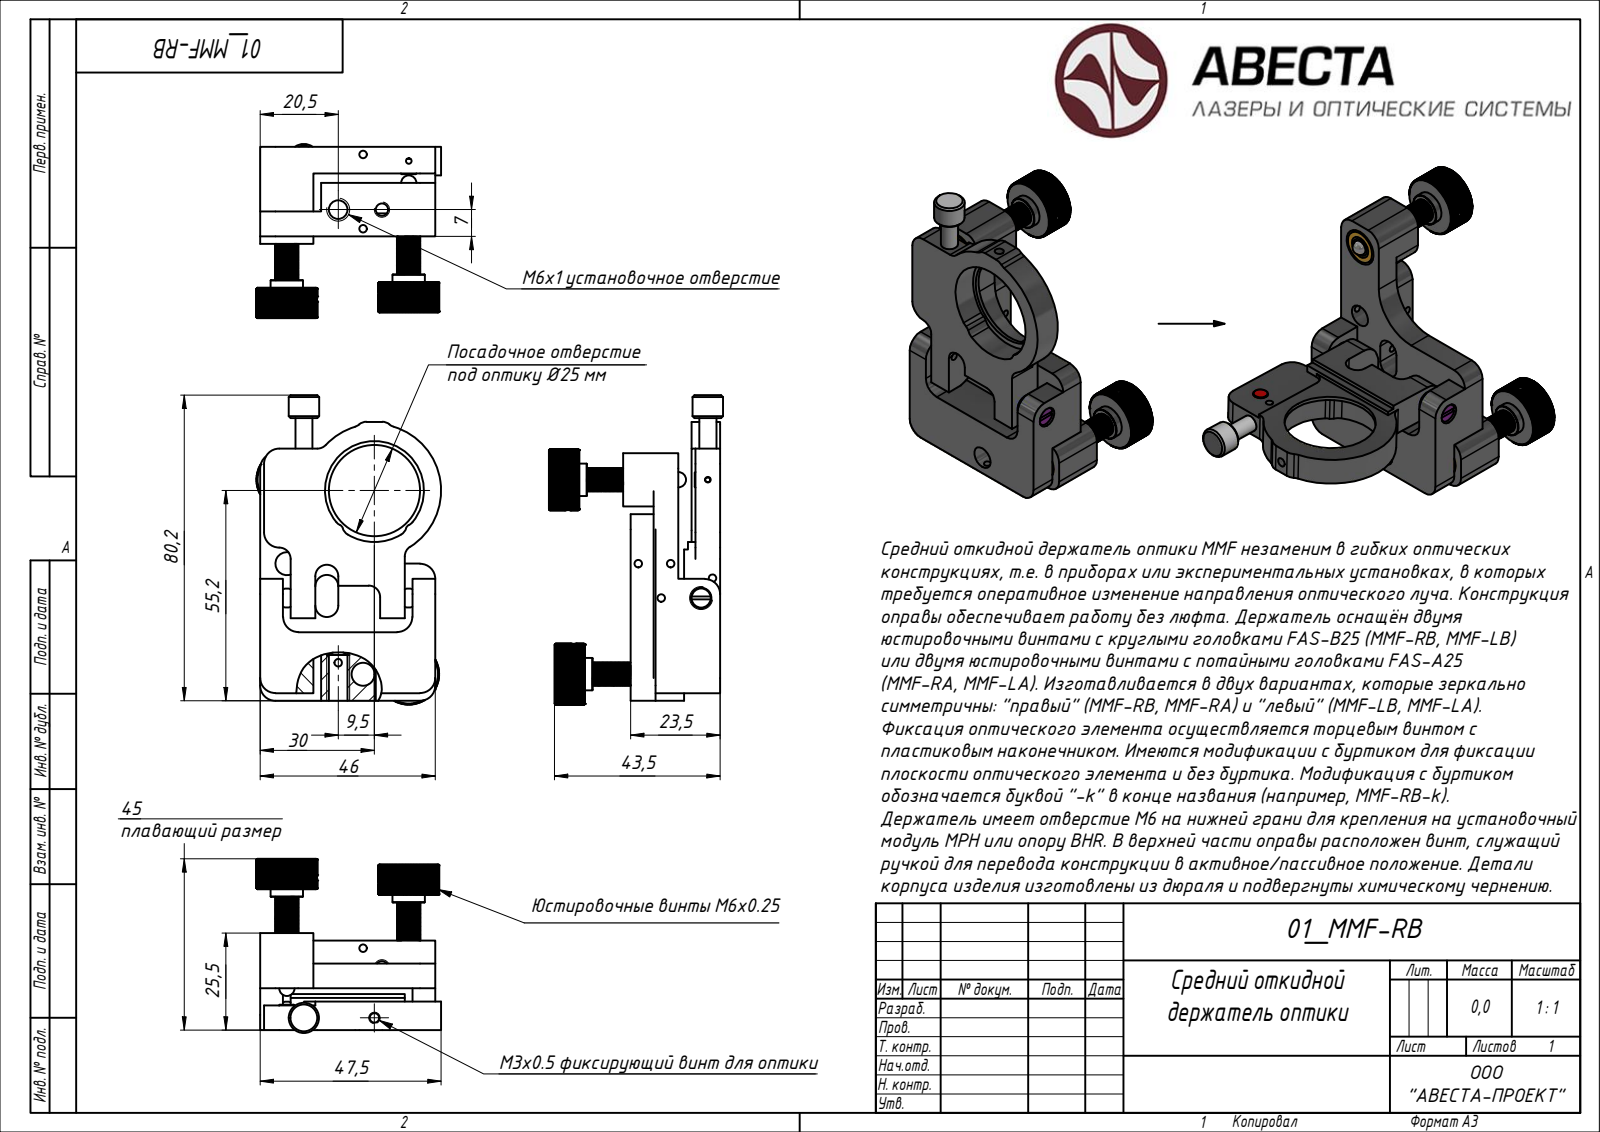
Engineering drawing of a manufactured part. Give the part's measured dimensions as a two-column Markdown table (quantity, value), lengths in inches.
| quantity | value |
| --- | --- |
| STEP written by | ST-DEVELOPER v15 (AUTOMOTIVE_DESIGN) |
| units | inches |
| bodies | 18 solids, 765 faces (319 planar, 0 cylindrical, 446 other) |
| overall size | 3.197 × 1.909 × 1.652 |
| volume | 2.494 in³ |
| surface area | 38.75 in² |
| main face-to-face distances | 0.256, 0.236, 0.079, 0.02, 0.551, 0.315, 0.433, 0.63, 0.295, 0.689 |
